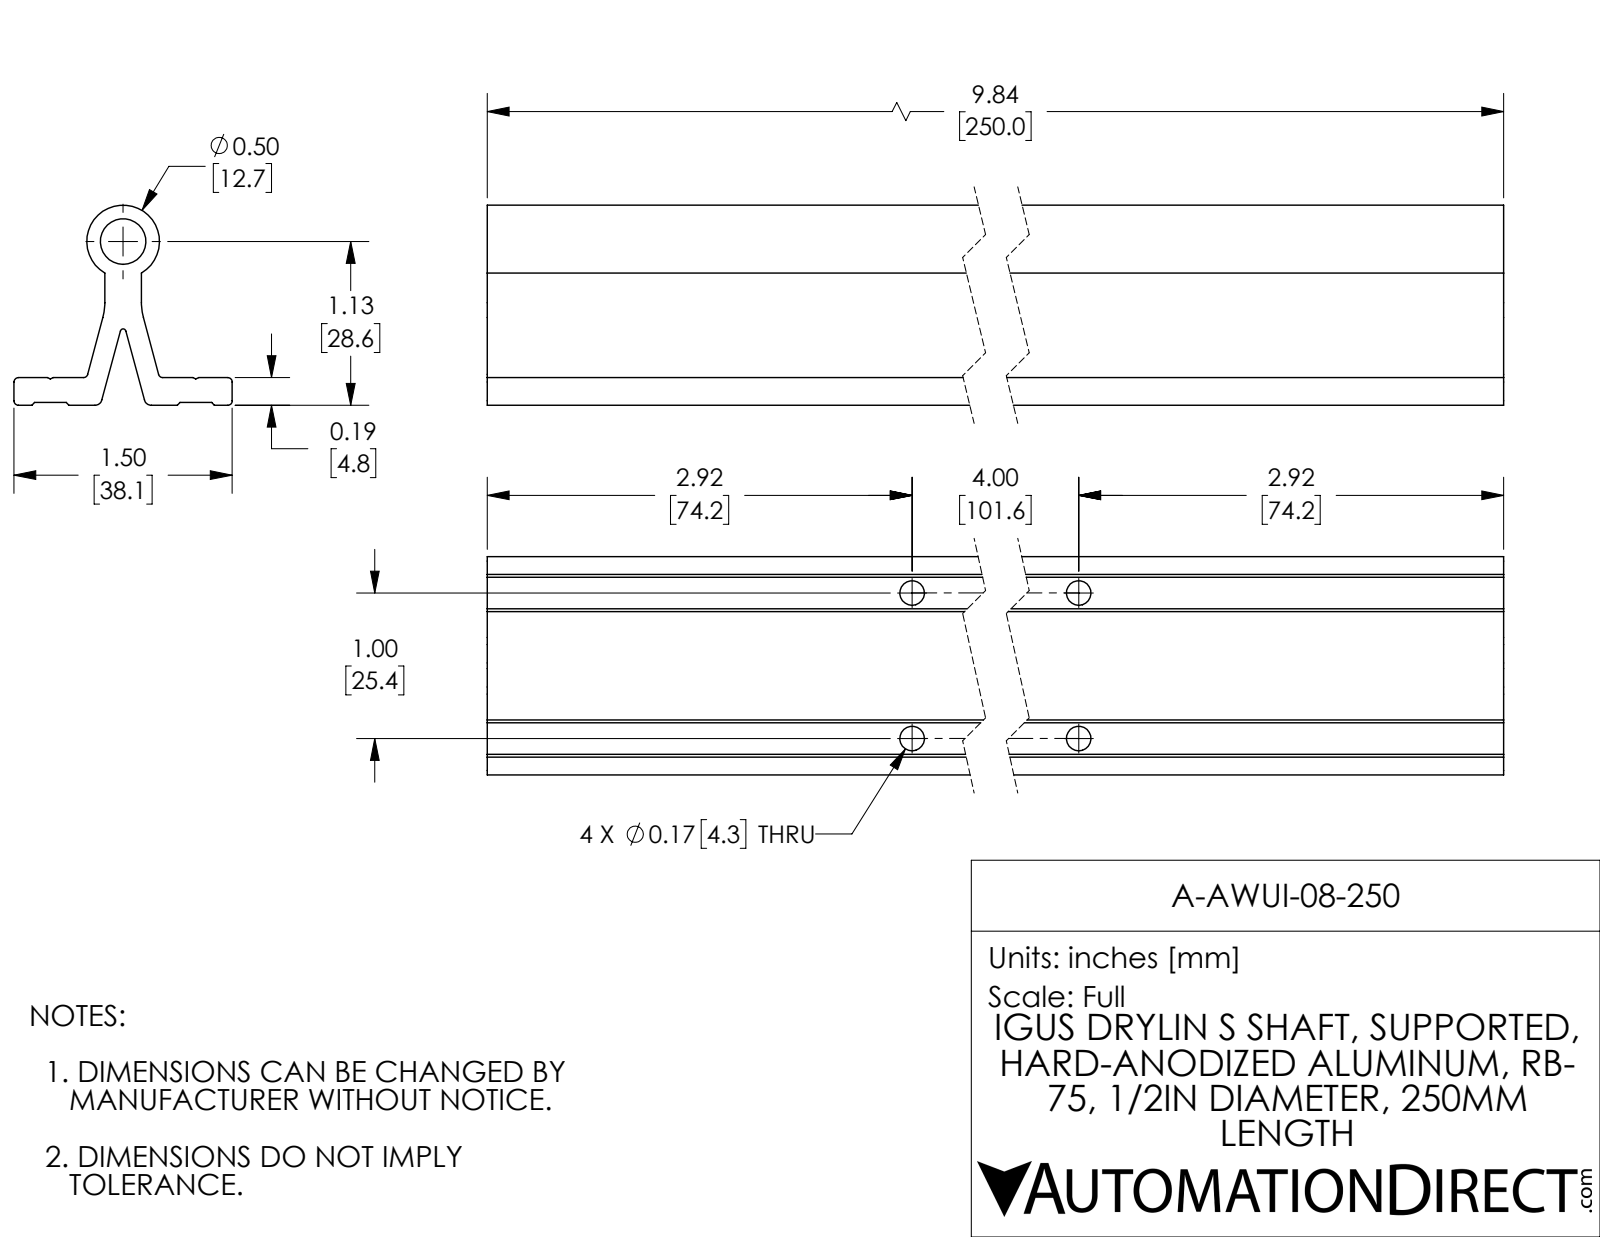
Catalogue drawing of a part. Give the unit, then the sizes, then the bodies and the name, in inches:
Units: inches
Overall size (bounding box): 9.843 × 1.5 × 1.375
Round holes (diameter × count): ⌀0.169 ×4, ⌀0.313 ×1
Round bosses / shafts (diameter × count): ⌀0.5 ×1
Partial cylindrical surfaces — rounded edges, fillets, slot ends (radius × count): R0.03 ×6, R0.05 ×2, R0.394 ×2, R0.02 ×1
Main face-to-face distances: 0.14, 0.19, 0.019, 0.171, 0.624, 0.876, 0.252, 1.5, 9.843, 0.707
Hole centre spacings: 1, 4, 4.123
Volume: 5.271 in³ · Surface area: 73.98 in²
Bodies: 1 solid, 58 faces (36 planar, 22 cylindrical, 0 other)
Part name (STEP PRODUCT): A-AWUI-08-250
STEP written by: SolidWorks 2017 (AUTOMOTIVE_DESIGN)
